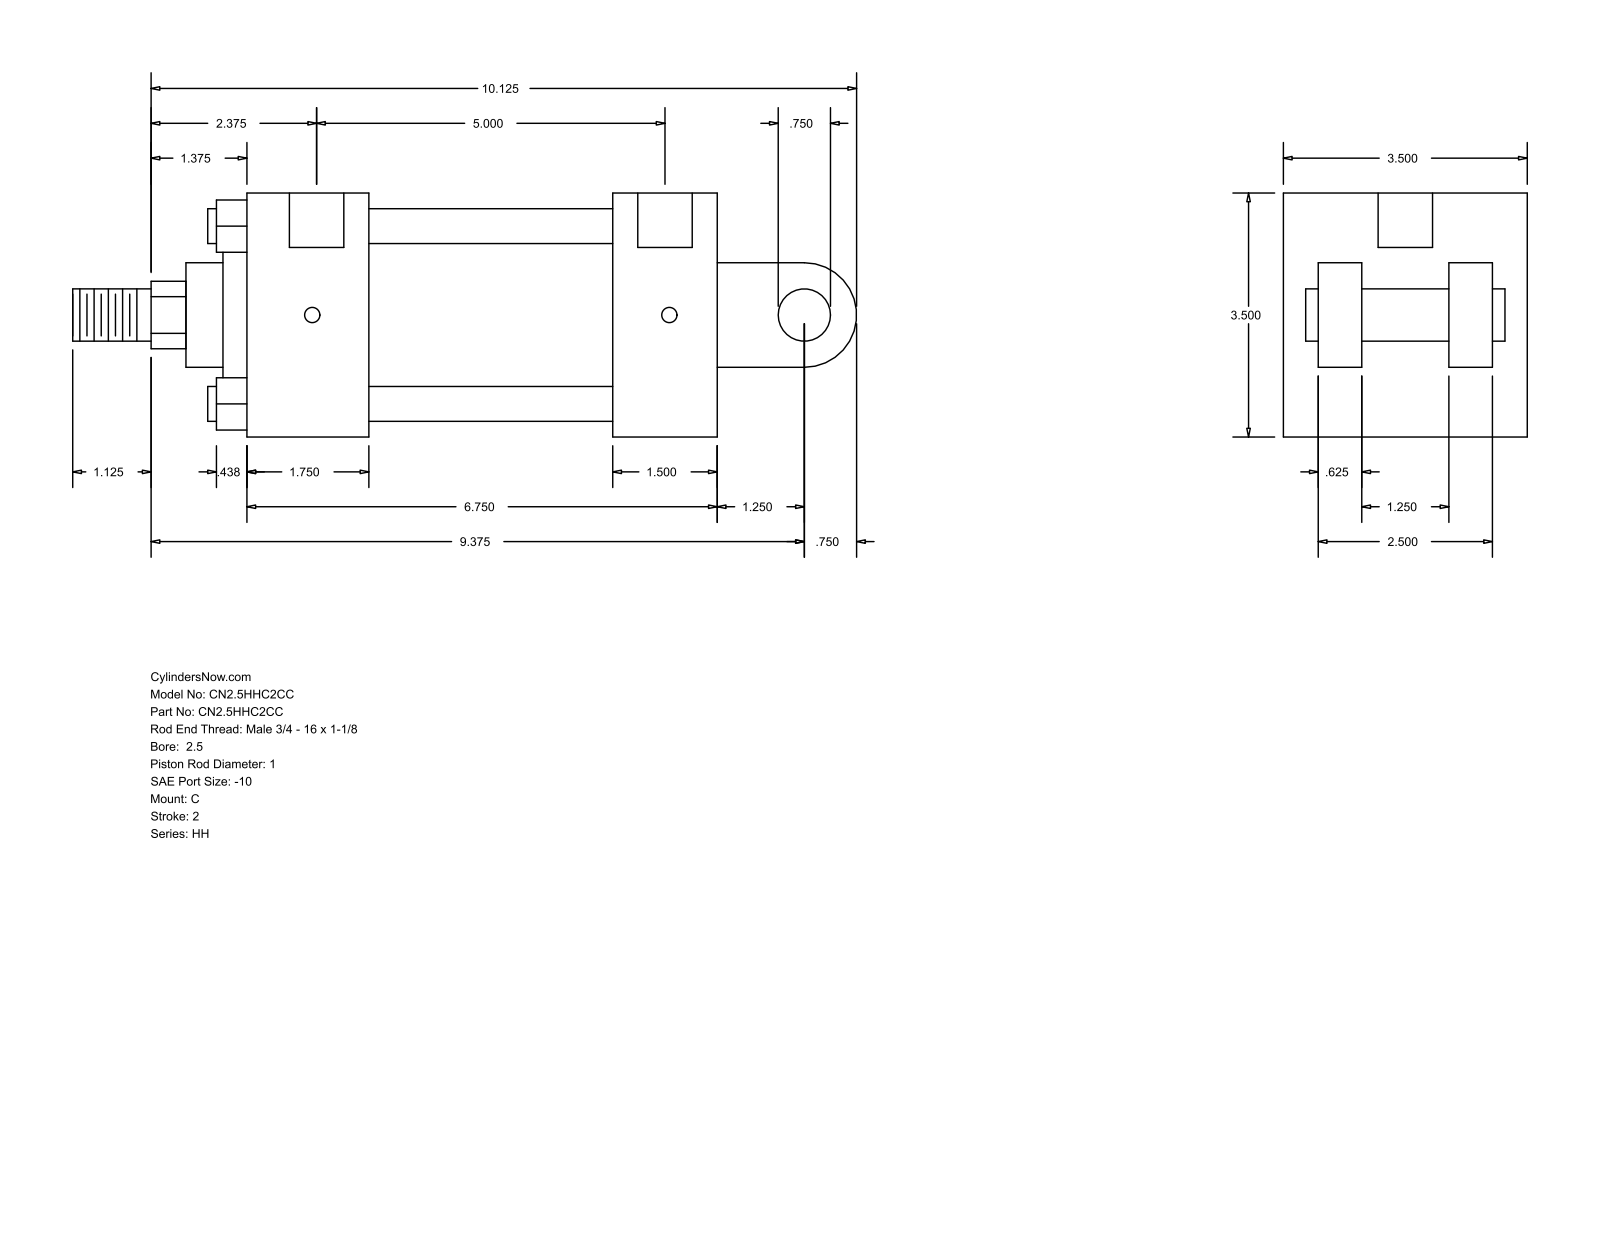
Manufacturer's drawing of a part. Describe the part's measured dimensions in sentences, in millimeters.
The part is named "HH_C__0250_1". Its 3-D file was written by "GSSL Pune (CONFIG_CONTROL_DESIGN)". It is 0 solids with 101 faces: 71 planar, 30 cylindrical and 0 other. Overall it measures 285.75 by 88.9 by 88.9 millimeters. Round holes: 4 of diameter 5.56, 2 of diameter 19.84. Round bosses or shafts: 4 of diameter 12.7, 2 of diameter 19.05, 1 of diameter 73.03, 1 of diameter 60.33, 1 of diameter 38.1, 1 of diameter 25.4. Partial cylindrical surfaces (rounded edges, fillets, slot ends): 1 of radius 12.29, 1 of radius 19.05. The main face-to-face distances are 88.9, 38.1, 171.46, 63.5, 133.36, 44.46, 127, 12.7, 28.57, 76.2. The hole center spacings are 1.59, 128.58, 130.17, 126.99.
